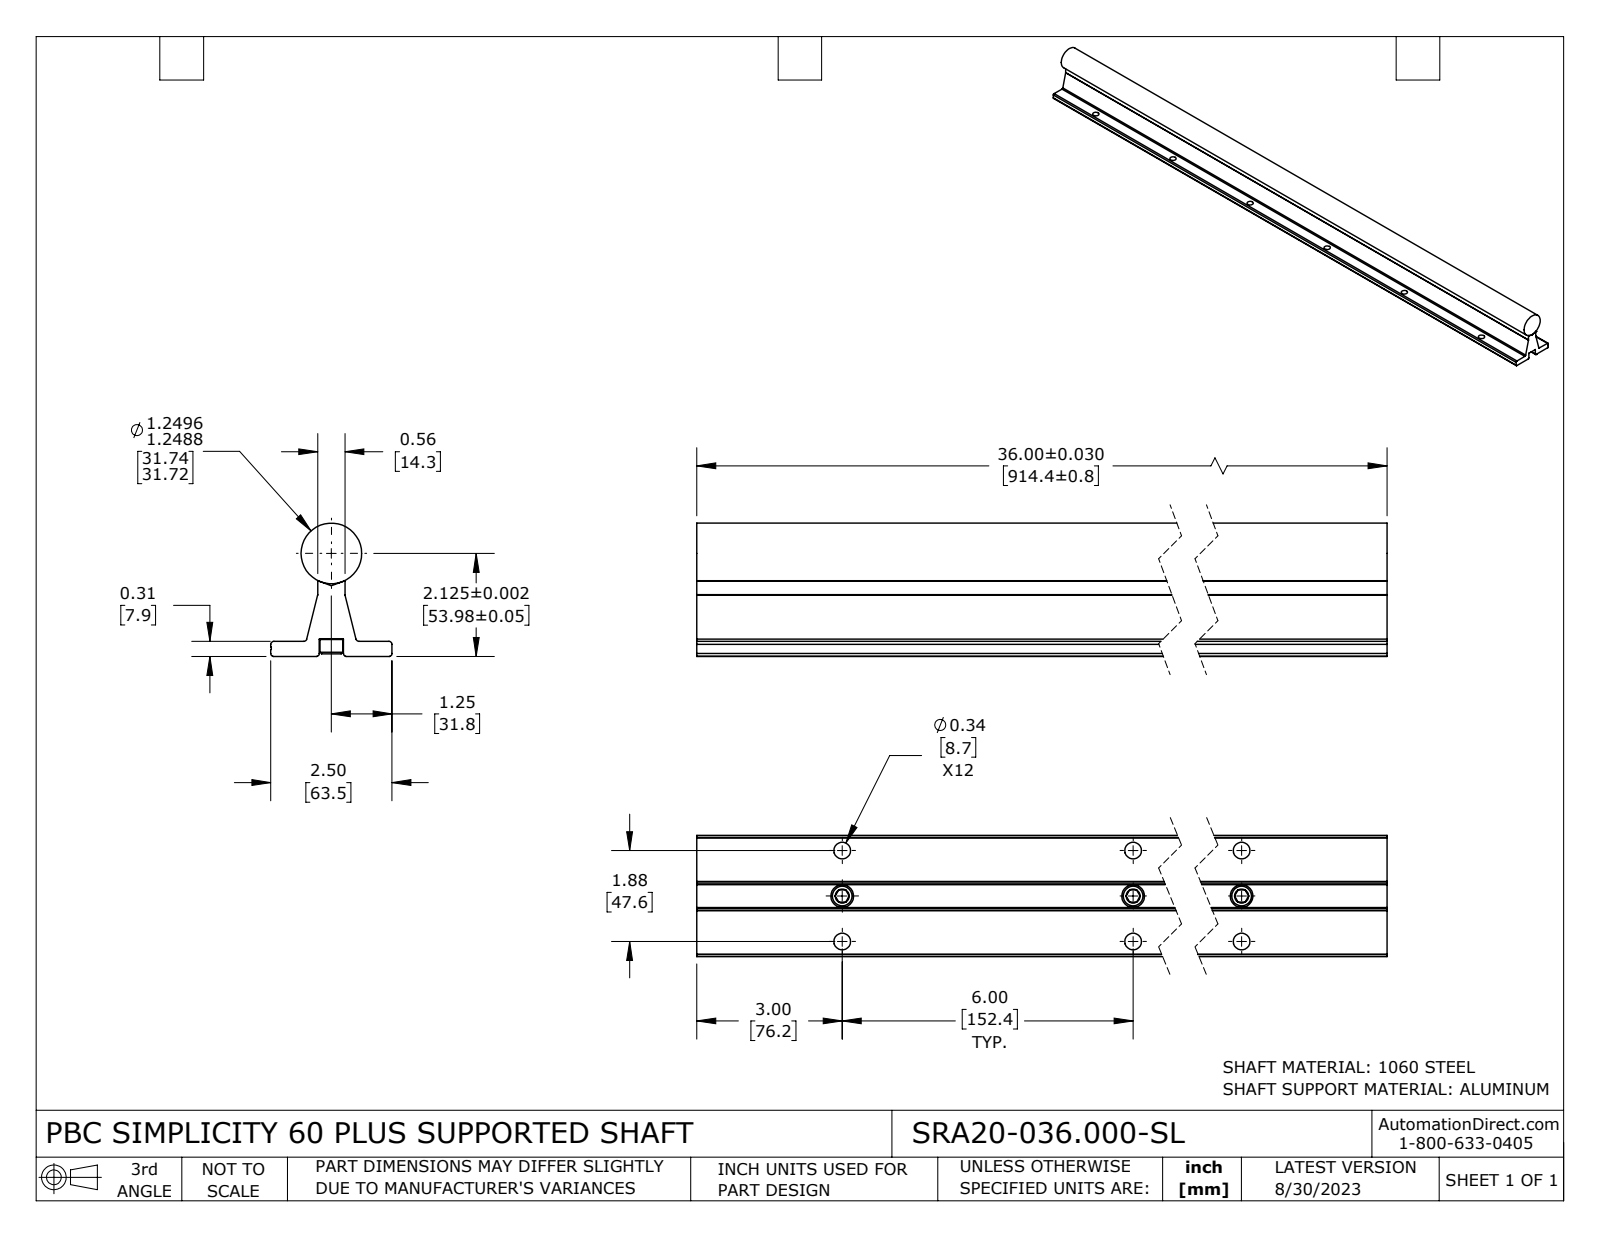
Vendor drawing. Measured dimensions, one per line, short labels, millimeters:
name: SRA20-036.000-SL
written by: SolidWorks 2021 (CONFIG_CONTROL_DESIGN)
unit: mm
bodies: 8 solids, 283 faces (93 planar, 100 cylindrical, 90 other)
size: 914.4 × 69.9 × 63.5
volume: 1 602 000 mm³; area: 305 600 mm²
holes: 18× ⌀8.7, 6× ⌀6.9, 6× ⌀9.5
bosses: 6× ⌀11.9, 6× ⌀8, 1× ⌀31.8
rounds: 6× R1.6, 3× R1.6, 2× R0.4, 2× R0.8, 1× R1.6
face distances: 8, 0.8, 13.5, 9.3, 1.4, 24.6, 25.4, 38.1, 38.9, 12.7
hole spacings: 154.3, 305.7, 152.4, 23.8, 304.8, 457.8, 159.7, 457.2
